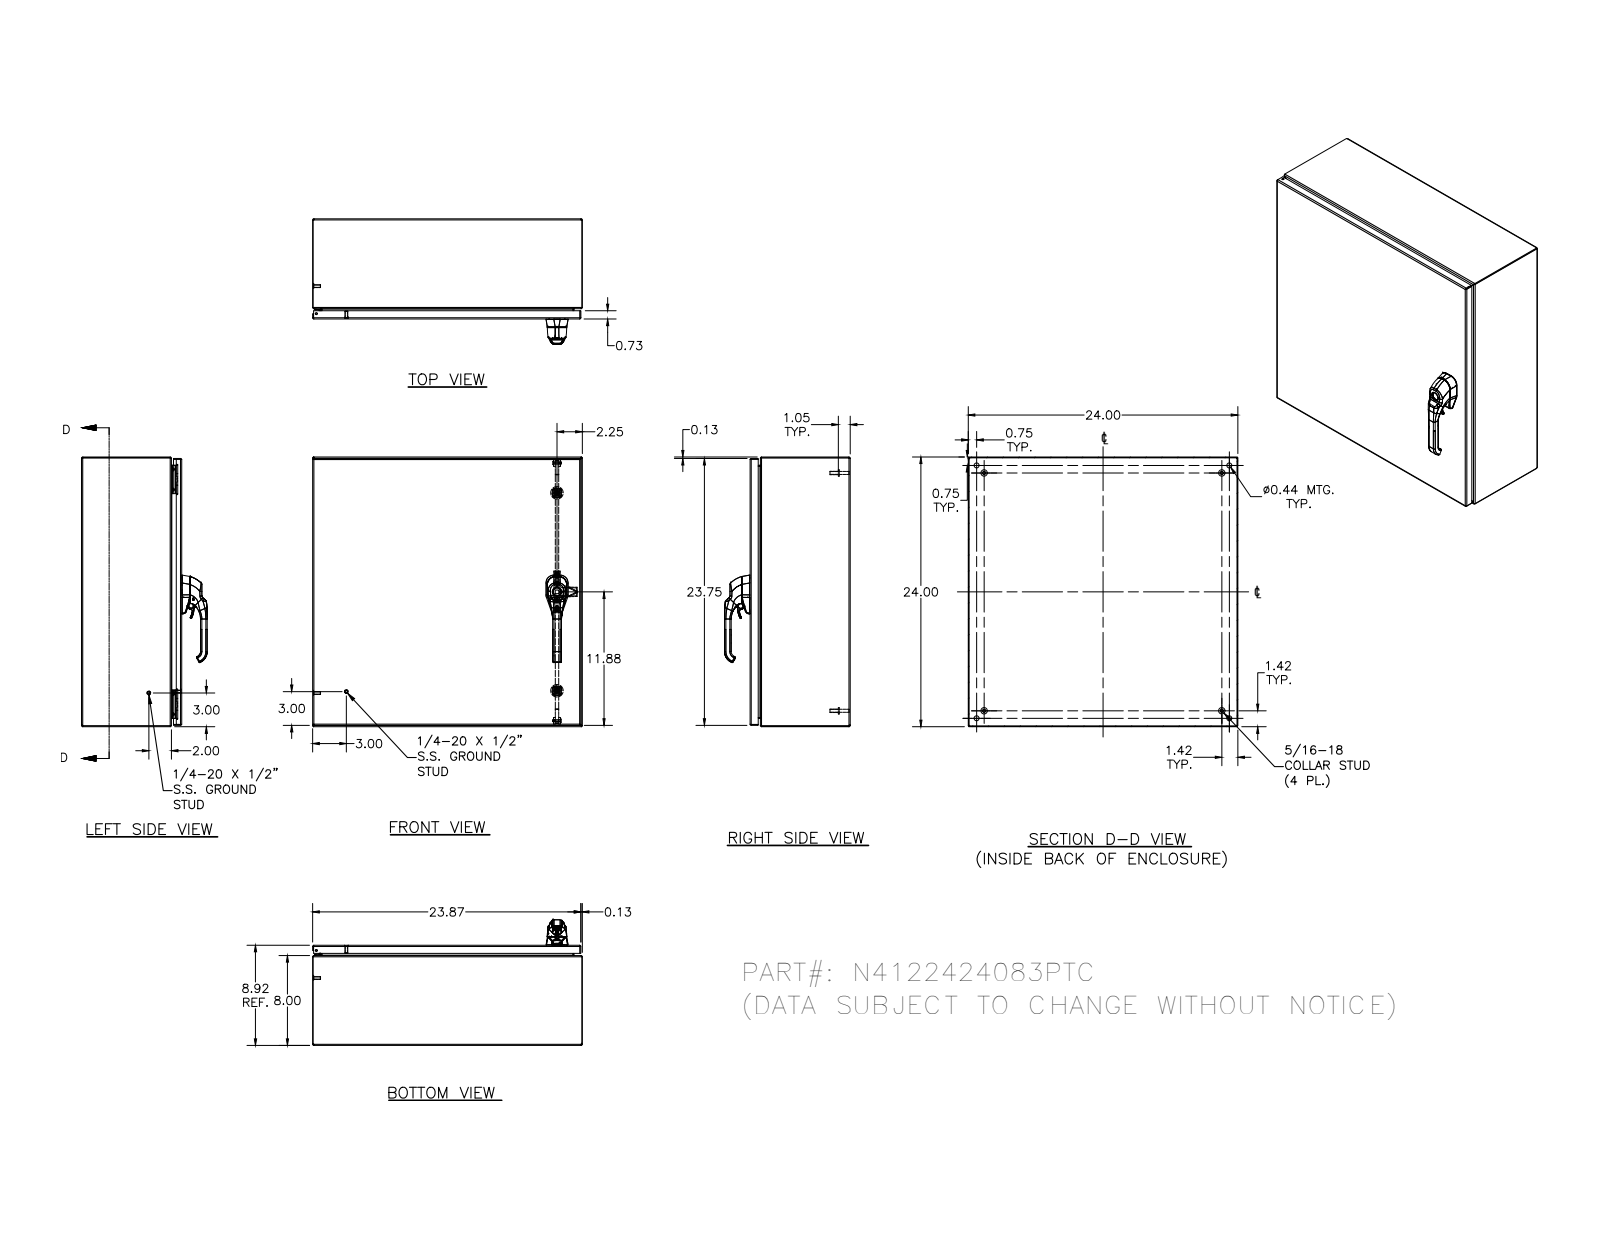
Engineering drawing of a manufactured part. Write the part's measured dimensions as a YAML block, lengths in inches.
part_name: "N4122424083PTC"
step_written_by: "SolidWorks 2018 (AUTOMOTIVE_DESIGN)"
units: inches
bodies: {solids: 51, faces: 1644, planar: 589, cylindrical: 592, other: 463}
overall_size: [24, 24, 11.095]
volume: 169.5
surface_area: 4334
round_holes:
  - {diameter: 0.188, count: 5}
  - {diameter: 0.093, count: 4}
  - {diameter: 0.152, count: 4}
  - {diameter: 0.165, count: 4}
  - {diameter: 0.167, count: 4}
  - {diameter: 0.172, count: 4}
  - {diameter: 0.197, count: 4}
  - {diameter: 0.437, count: 4}
  - {diameter: 0.106, count: 2}
  - {diameter: 0.156, count: 2}
  - {diameter: 0.16, count: 2}
  - {diameter: 0.169, count: 2}
round_bosses_or_shafts:
  - {diameter: 0.25, count: 10}
  - {diameter: 0.563, count: 4}
  - {diameter: 0.36, count: 4}
  - {diameter: 0.32, count: 4}
  - {diameter: 0.3, count: 4}
  - {diameter: 0.275, count: 4}
  - {diameter: 0.256, count: 4}
  - {diameter: 0.236, count: 4}
partial_cylinders:
  - {radius: 0.031, count: 30}
  - {radius: 0.05, count: 26}
  - {radius: 0.105, count: 20}
  - {radius: 0.016, count: 18}
  - {radius: 0.02, count: 18}
  - {radius: 0.118, count: 16}
  - {radius: 0.125, count: 14}
  - {radius: 0.032, count: 8}
face_to_face_distances: [0.074, 8.843, 23.926, 8.917, 8.769, 23.852, 24, 7.926, 0.917, 0.739]
hole_center_spacings: [19.996, 22.5, 22.869, 0.017, 0.66, 20.656, 0.019, 0.5]
